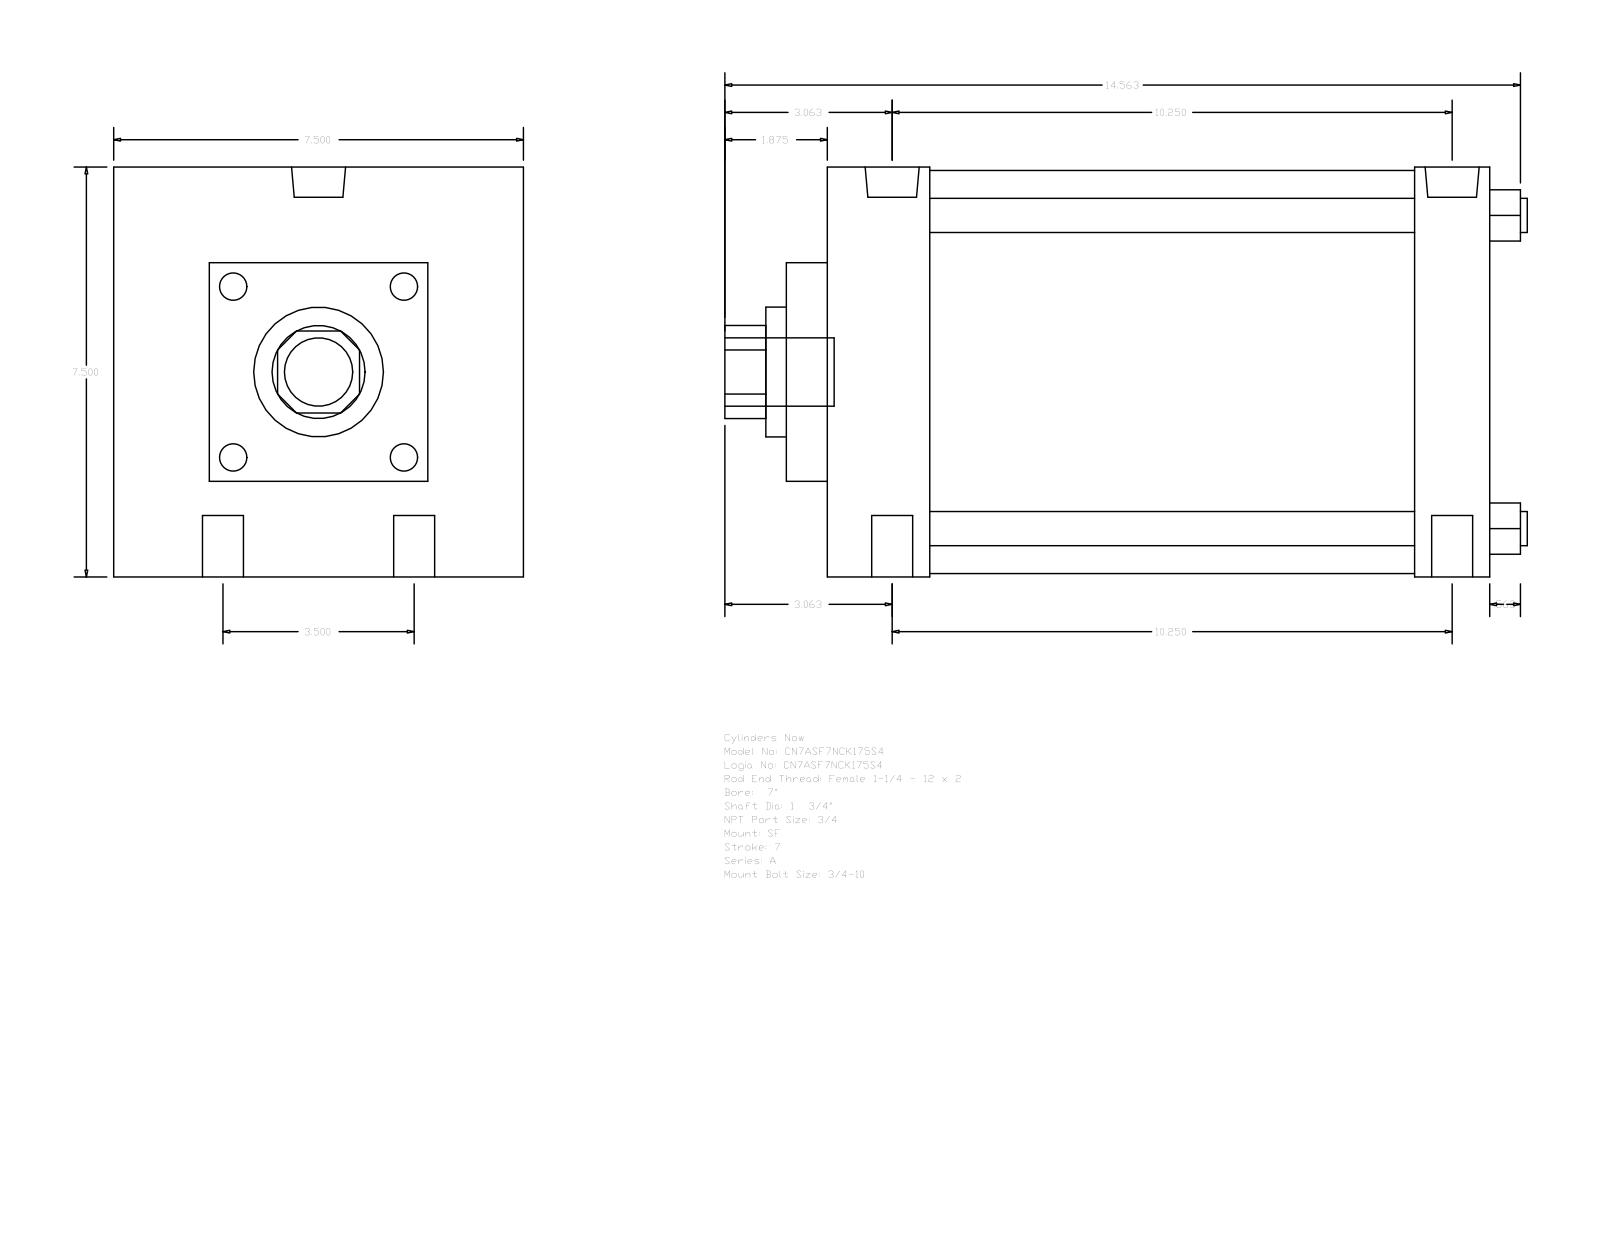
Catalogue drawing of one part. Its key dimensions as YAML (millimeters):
part_name: "A_SF__0700_1.75"
step_written_by: "GSSL Pune (CONFIG_CONTROL_DESIGN)"
units: millimeters
bodies: {solids: 0, faces: 93, planar: 67, cylindrical: 26, other: 0}
overall_size: [373.06, 190.5, 190.5]
round_holes:
  - {diameter: 19.05, count: 4}
  - {diameter: 15.08, count: 2}
  - {diameter: 25.12, count: 2}
  - {diameter: 44.45, count: 1}
  - {diameter: 60.33, count: 1}
round_bosses_or_shafts:
  - {diameter: 15.88, count: 4}
  - {diameter: 187.32, count: 1}
  - {diameter: 31.75, count: 1}
partial_cylinders:
  - {radius: 21.63, count: 1}
face_to_face_distances: [190.5, 307.98, 44.45, 34.92, 19.05, 47.63, 273.06, 225.43, 260.35, 146.05]
hole_center_spacings: [44.45, 264.12, 260.35, 88.9, 275.11, 249.23]
